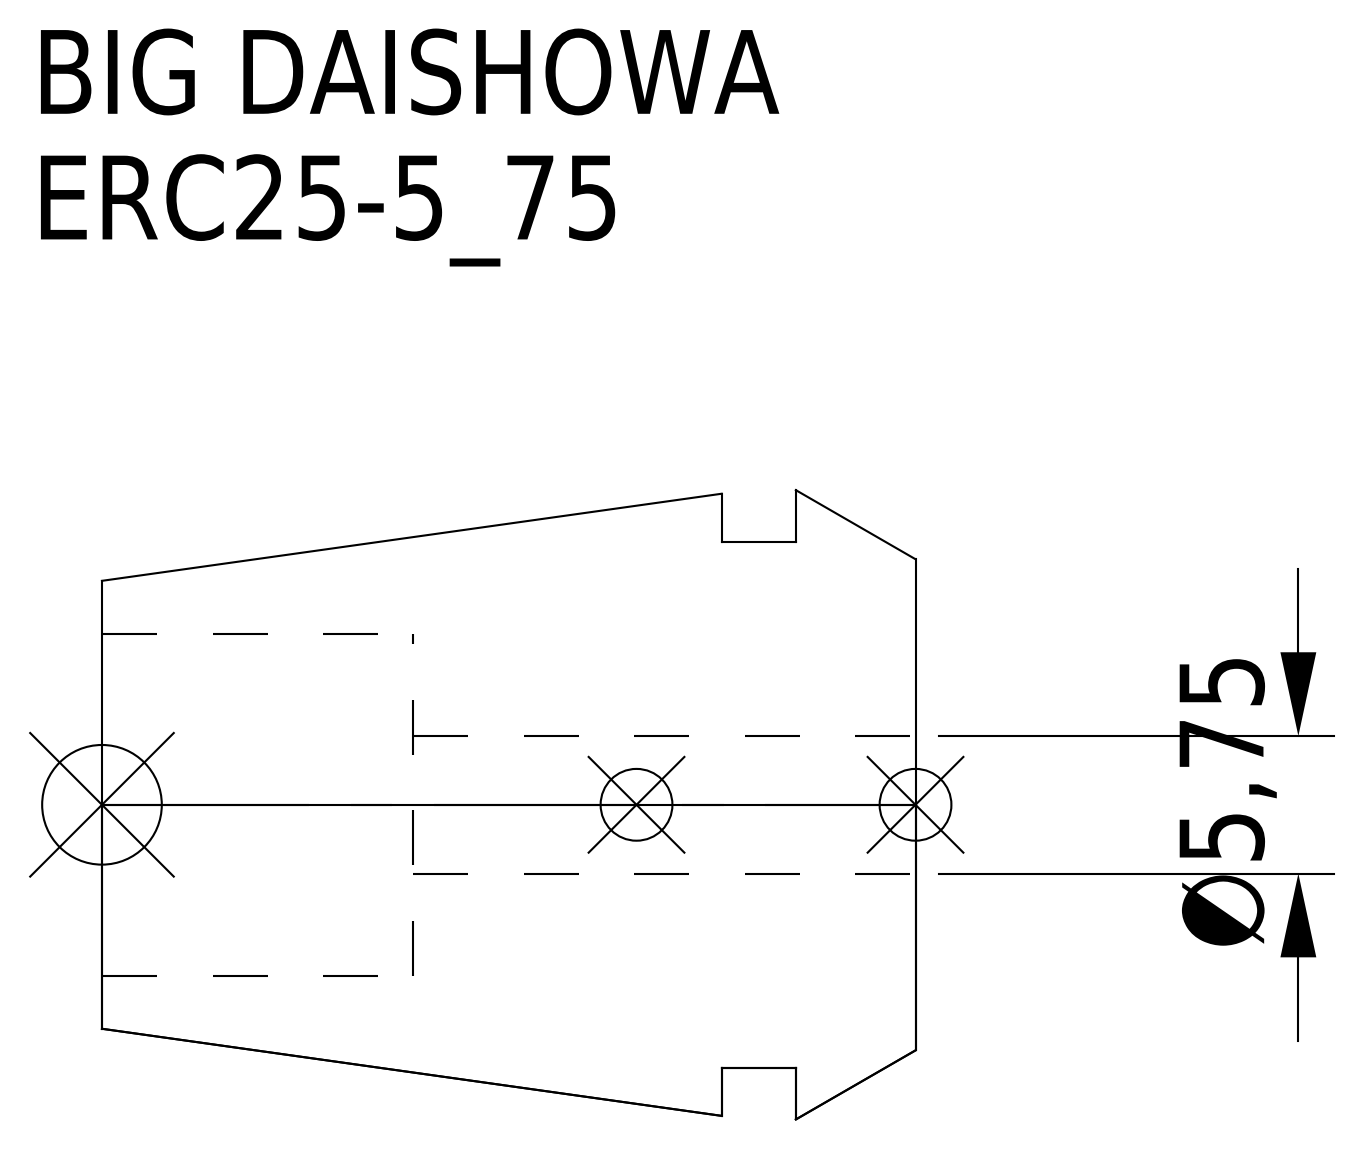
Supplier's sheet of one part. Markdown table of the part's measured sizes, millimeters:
| quantity | value |
| --- | --- |
| part name | ERC25-5_75 |
| STEP written by | CREO PARAMETRIC BY PTC INC, 2016380 (AUTOMOTIVE_DESIGN) |
| units | millimeters |
| bodies | 1 solid, 15 faces (5 planar, 6 cylindrical, 4 other) |
| overall size | 34 × 26.3 × 26.3 |
| volume | 10 970 mm³ |
| surface area | 4 308 mm² |
| round holes (diameter × count) | 5.75 × 1, 14.3 × 1 |
| round bosses / shafts (diameter × count) | 22 × 1 |
| main face-to-face distances | 5, 8.1, 3.1, 21, 16, 12.9, 34, 29, 25.9, 13 |
